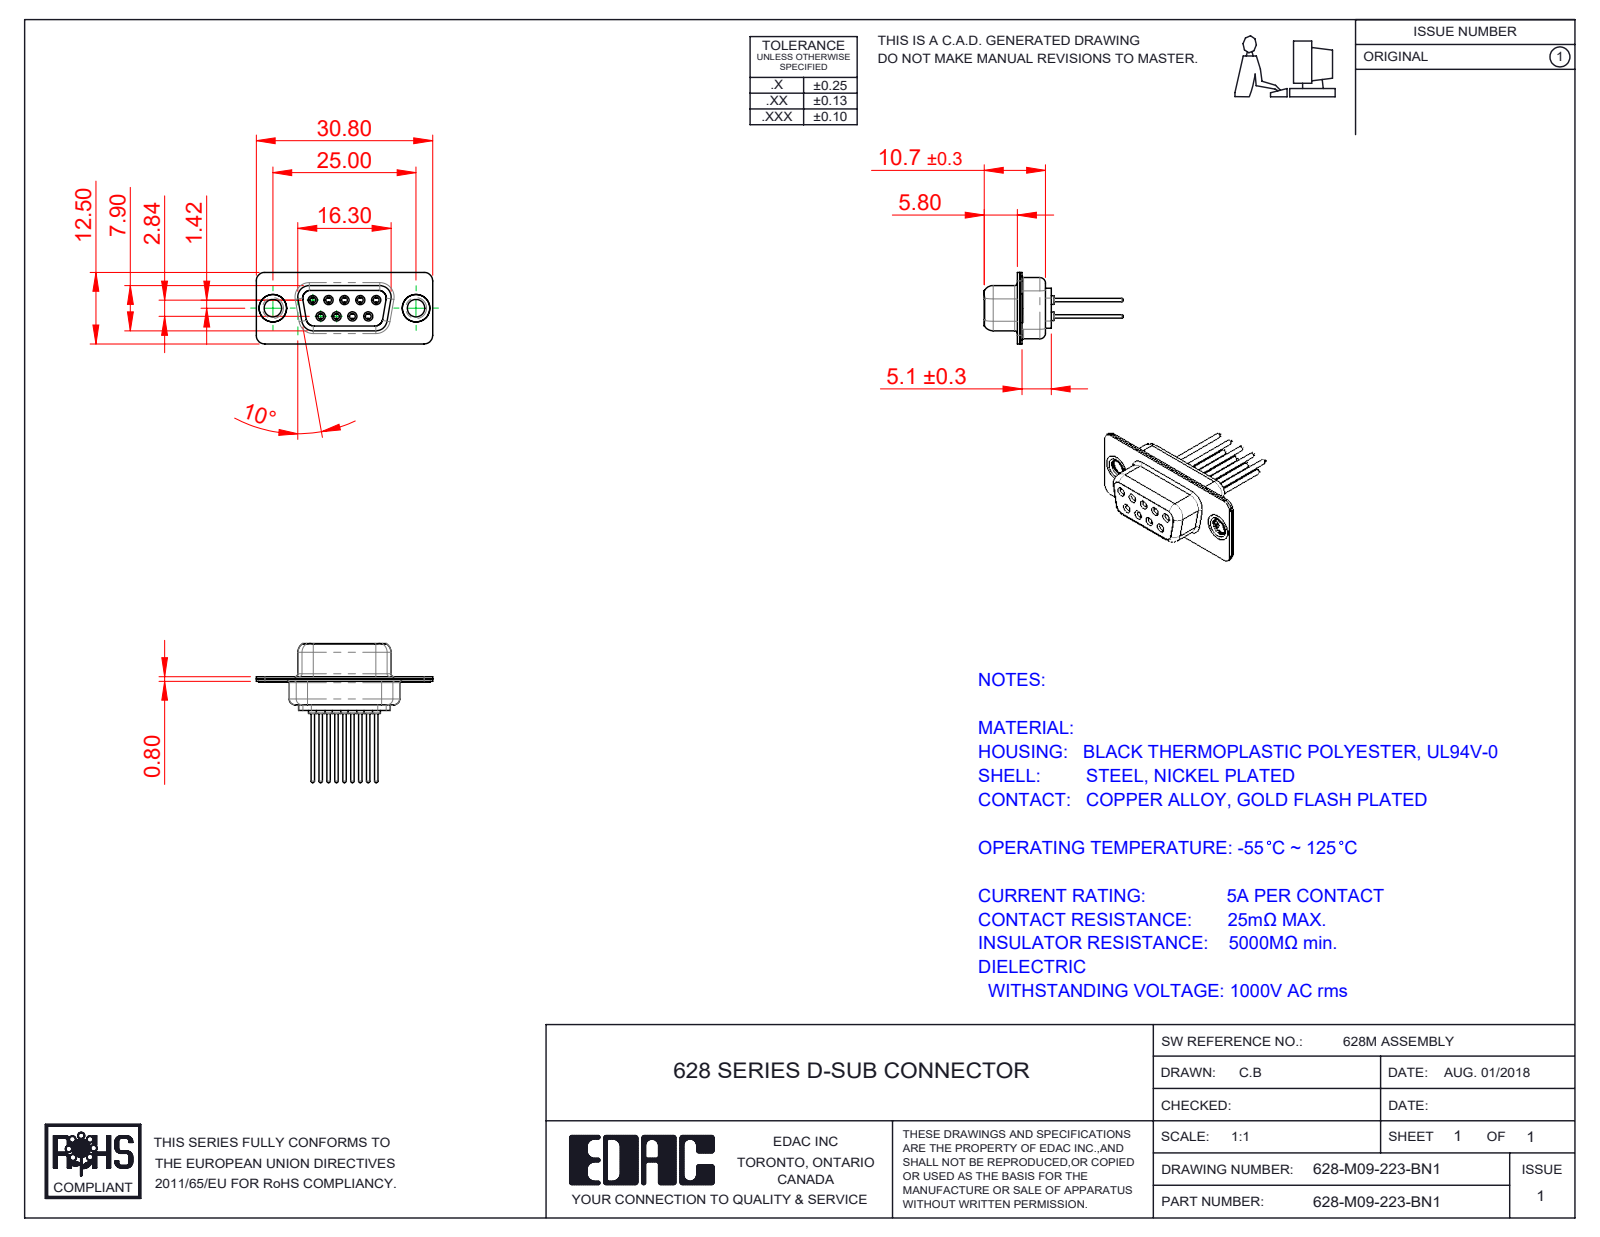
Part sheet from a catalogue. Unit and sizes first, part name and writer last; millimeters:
Units: millimetres
Overall size (bounding box): 30.8 × 24.27 × 12.5
Round holes (diameter × count): ⌀1 ×9, ⌀1.1 ×9, ⌀1.7 ×9, ⌀1.8 ×9, ⌀2 ×9, ⌀3.05 ×2, ⌀4 ×2, ⌀4.8 ×2
Round bosses / shafts (diameter × count): ⌀2.2 ×9, ⌀1.6 ×9, ⌀1.5 ×9, ⌀0.6 ×9, ⌀5 ×2, ⌀4.9 ×2, ⌀3.55 ×2
Partial cylindrical surfaces — rounded edges, fillets, slot ends (radius × count): R1.5 ×16, R2 ×12, R1.35 ×8, R1.6 ×8, R0.25 ×4, R0.5 ×4, R0.6 ×4, R0.65 ×4
Main face-to-face distances: 0.4, 1.4, 0.45, 8.45, 0.8, 8.9, 1.8, 1, 6.2, 1.35
Hole centre spacings: 3.16, 2.77, 5.54, 5.03, 5.04, 8.31, 7.1, 7.48
Volume: 1 641 mm³ · Surface area: 4 390 mm²
Bodies: 14 solids, 748 faces (202 planar, 292 cylindrical, 254 other)
Part name (STEP PRODUCT): 628M Housing_09 Contacts; 628M Contact Row 1_23; 628M Shell Rear_09 Contacts; 628M Contact Row 2_23 (+3 more)
STEP written by: SolidWorks 2020 (CONFIG_CONTROL_DESIGN)
